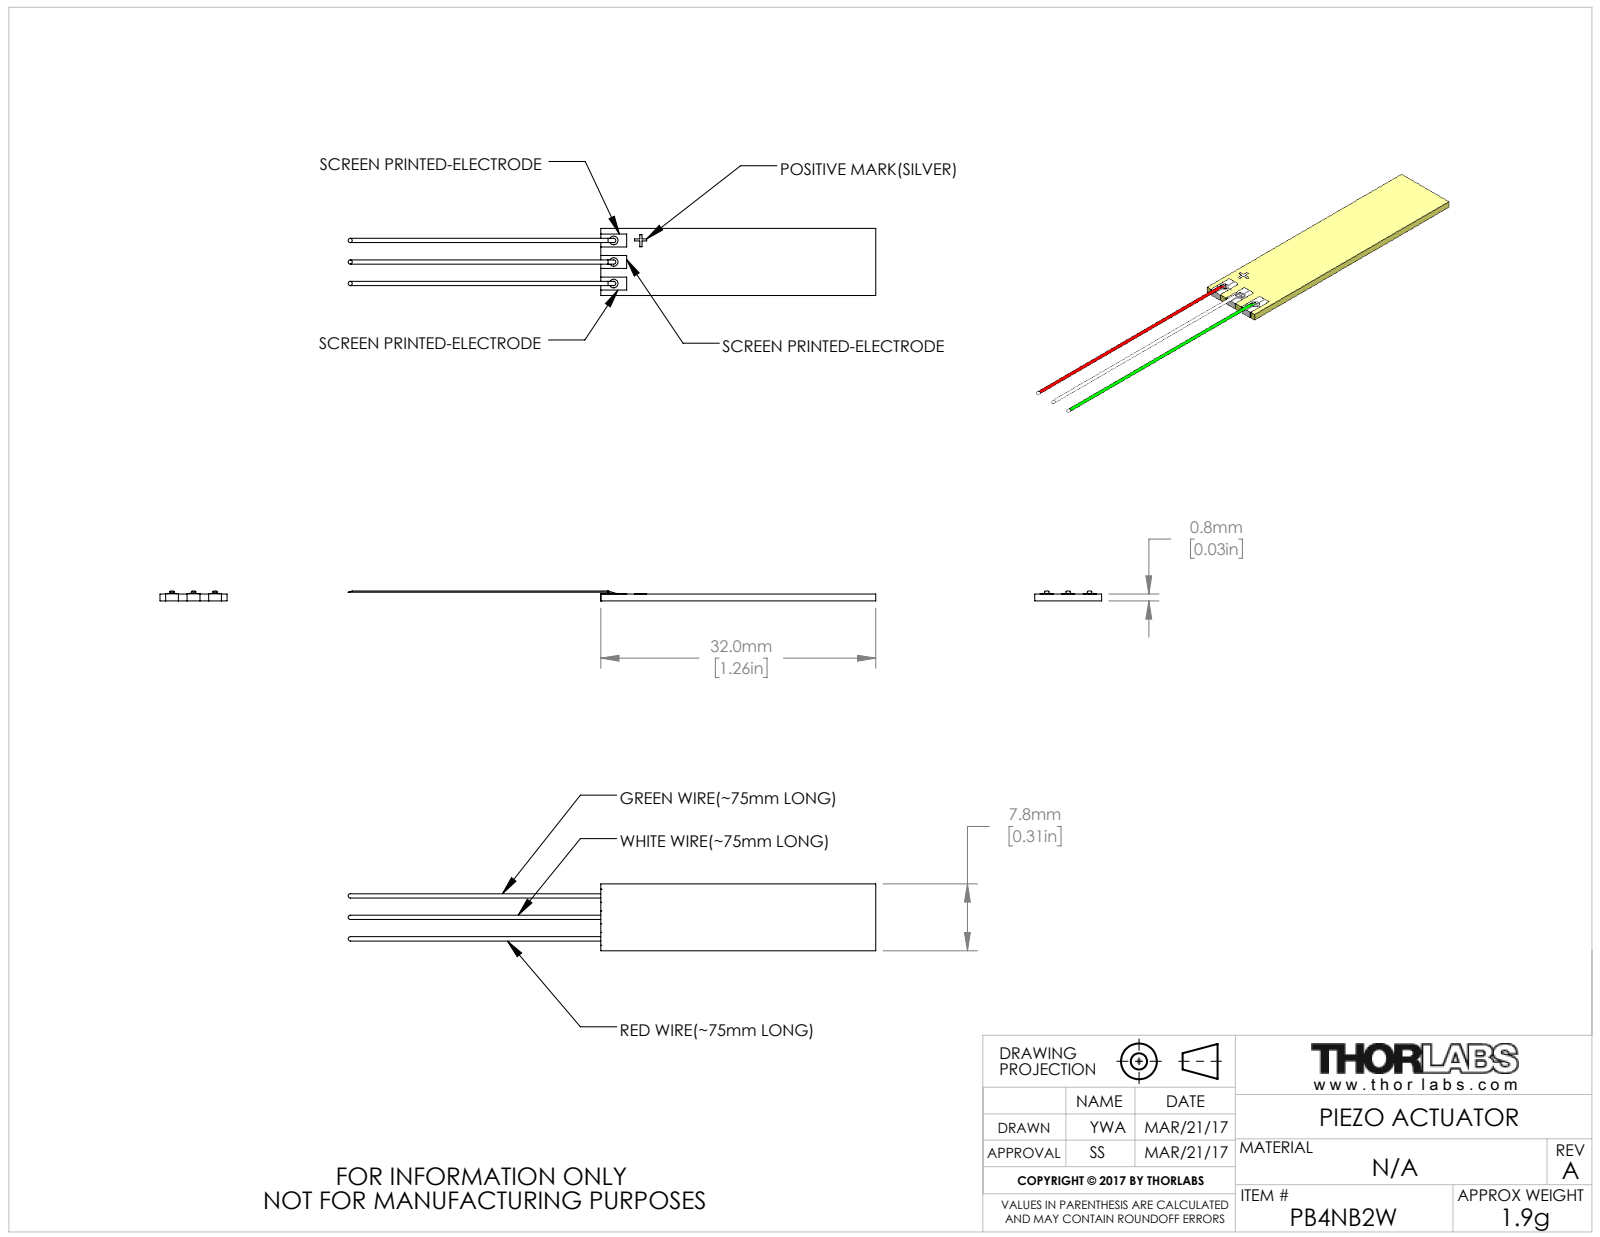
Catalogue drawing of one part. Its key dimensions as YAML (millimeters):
part_name: "CTN010296"
step_written_by: "SolidWorks 2016 (AUTOMOTIVE_DESIGN)"
units: millimeters
bodies: {solids: 1, faces: 63, planar: 45, cylindrical: 6, other: 12}
overall_size: [61.42, 7.8, 1.16]
volume: 205
surface_area: 665
round_bosses_or_shafts:
  - {diameter: 1, count: 3}
face_to_face_distances: [0.8, 7.8, 0.81, 32.01, 32, 0.86, 2.5, 1.5, 2.15, 3.15]
